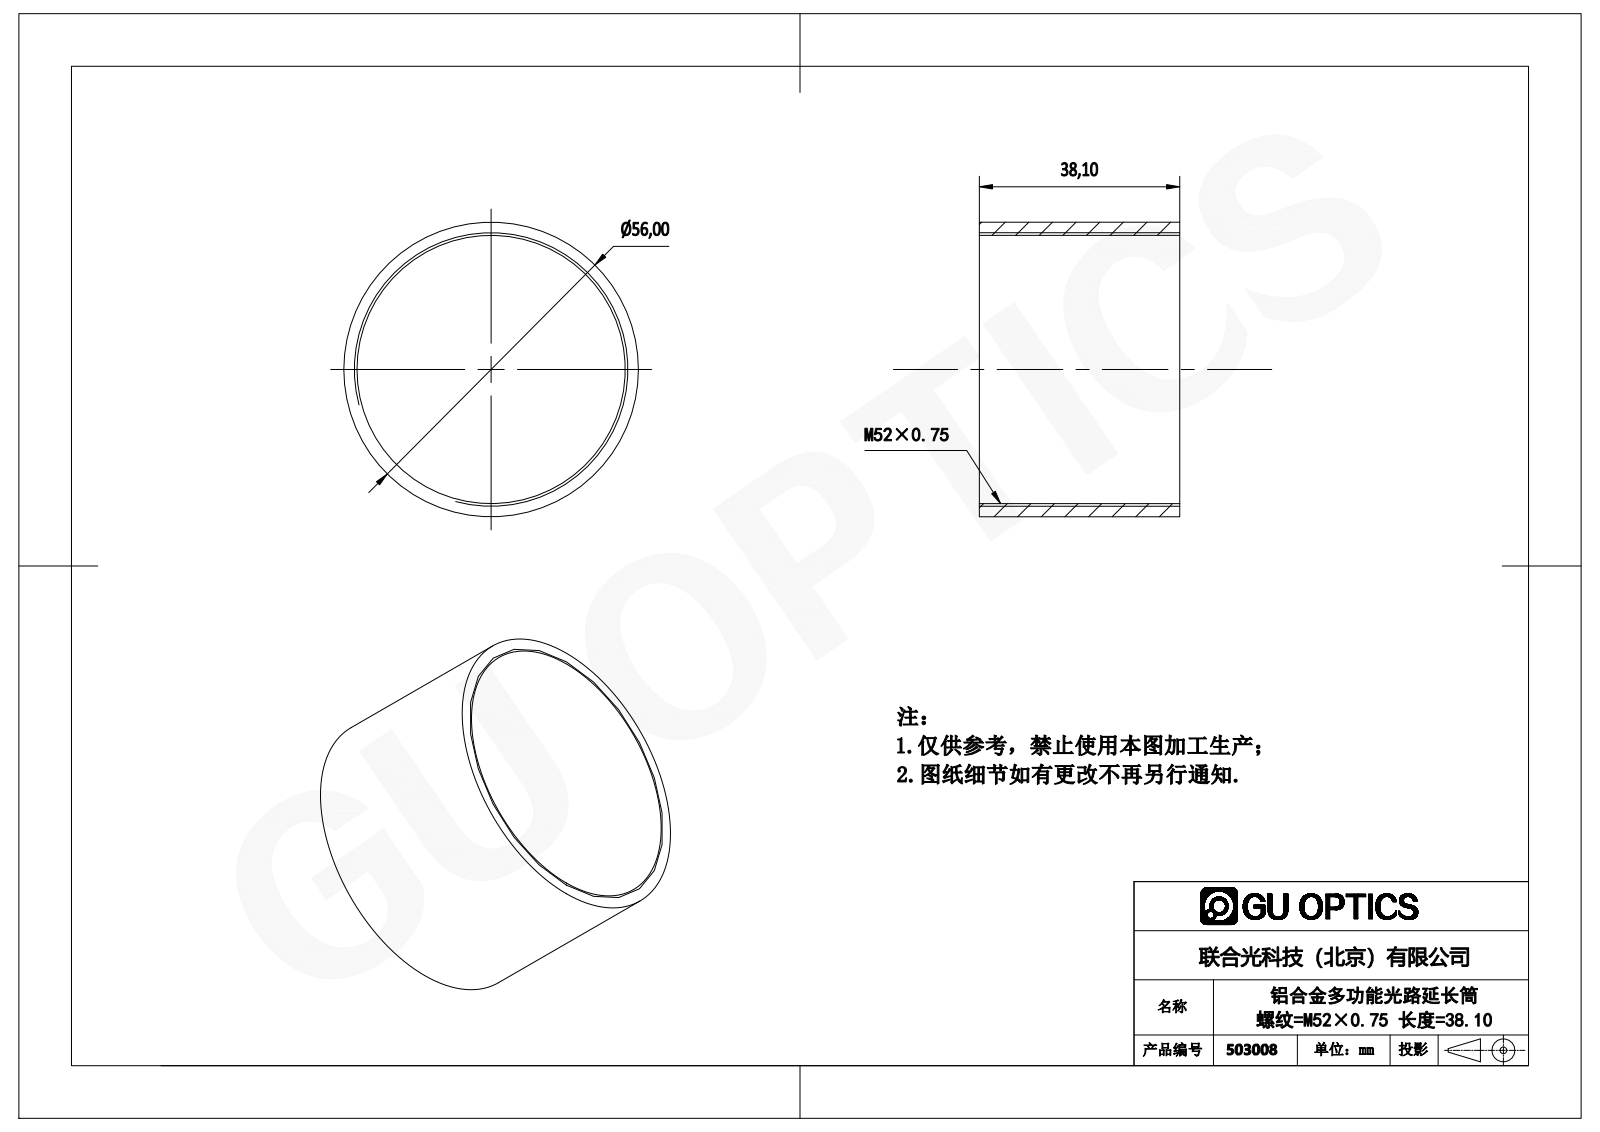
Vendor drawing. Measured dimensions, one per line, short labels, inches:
name: 503008
written by: SolidWorks 2016 (AUTOMOTIVE_DESIGN)
unit: in
bodies: 1 solid, 6 faces (2 planar, 4 cylindrical, 0 other)
size: 2.205 × 2.205 × 1.5
volume: 0.977 in³; area: 21.15 in²
holes: 1× ⌀2.008
bosses: 1× ⌀2.205
face distances: 1.5
